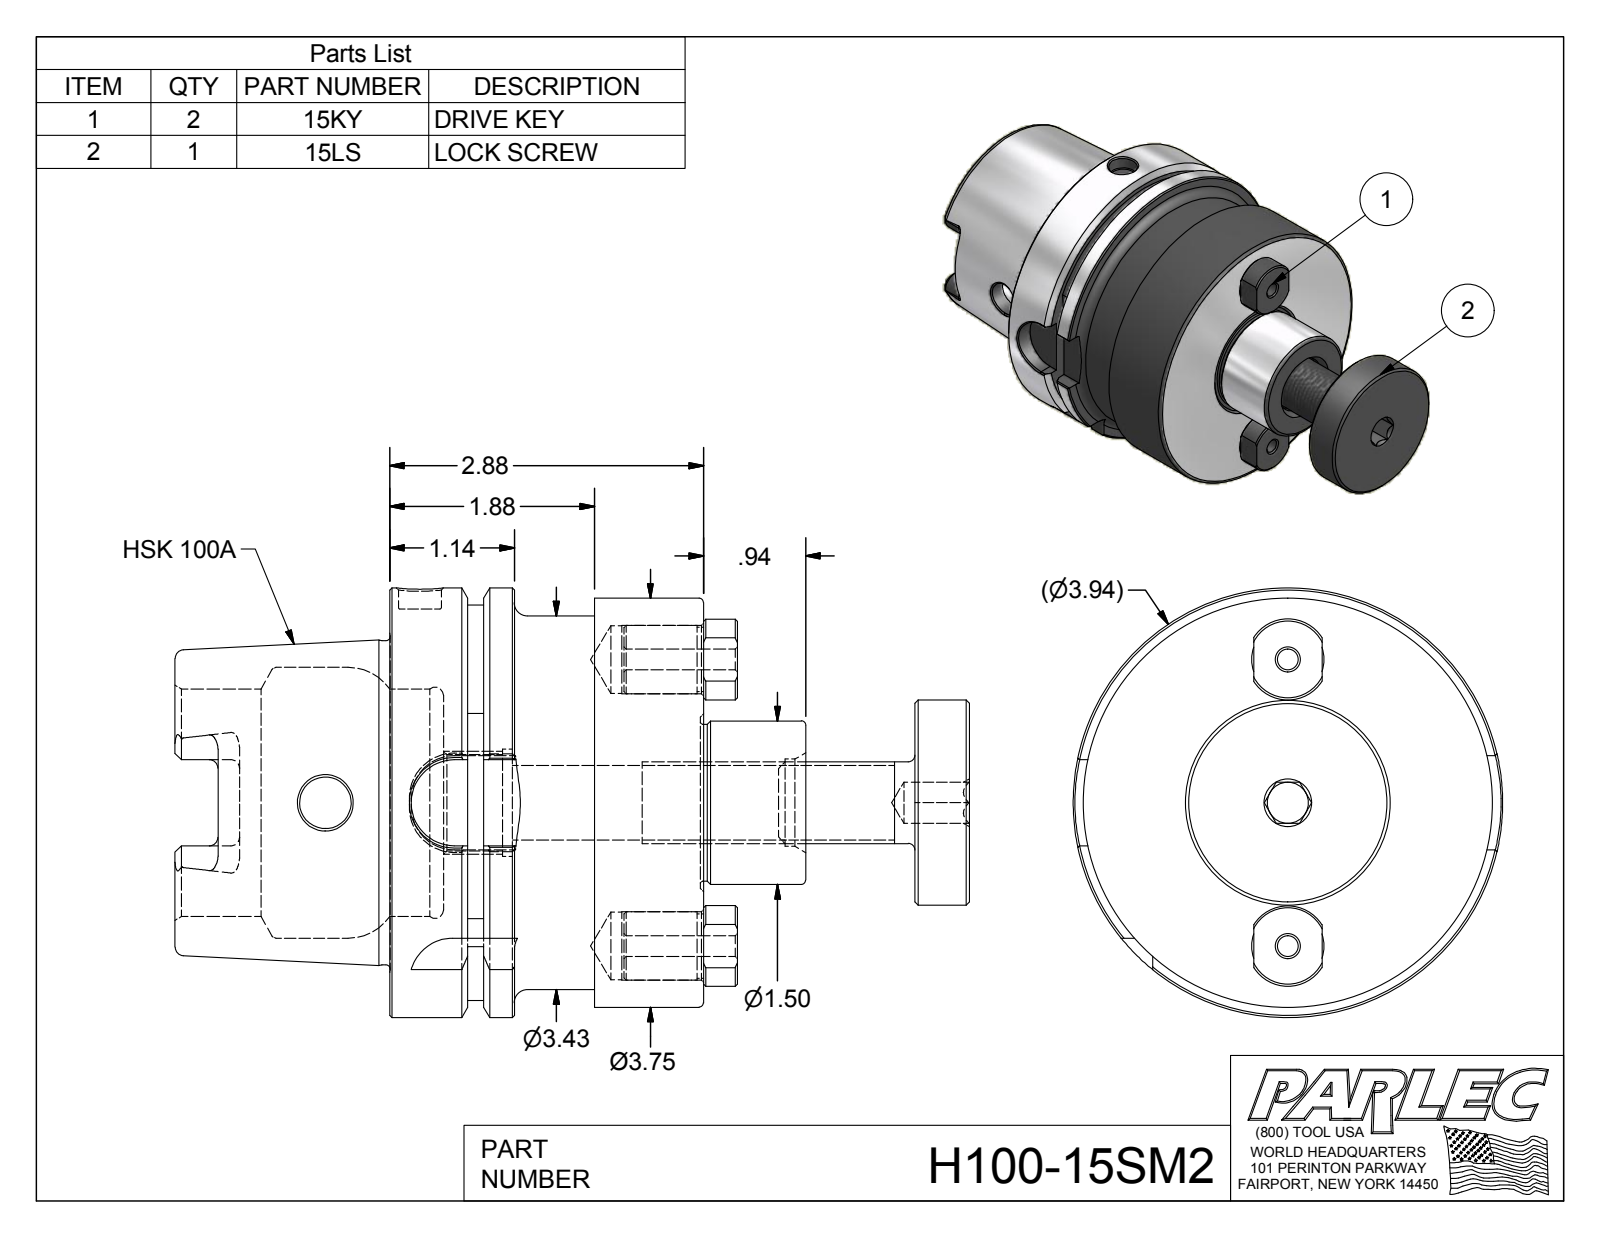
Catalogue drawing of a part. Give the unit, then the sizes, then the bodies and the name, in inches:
Units: inches
Overall size (bounding box): 7.281 × 3.937 × 3.937
Round holes (diameter × count): ⌀0.19 ×2, ⌀0.618 ×2, ⌀0.624 ×2, ⌀0.375 ×1, ⌀0.394 ×1, ⌀0.472 ×1, ⌀0.682 ×1, ⌀0.8 ×1, ⌀0.881 ×1, ⌀0.985 ×1, ⌀2.087 ×1, ⌀2.48 ×1
Round bosses / shafts (diameter × count): ⌀0.626 ×2, ⌀0.59 ×2, ⌀3.937 ×1, ⌀3.75 ×1, ⌀3.425 ×1, ⌀2.967 ×1, ⌀1.88 ×1, ⌀1.5 ×1
Partial cylindrical surfaces — rounded edges, fillets, slot ends (radius × count): R0.079 ×6, R0.192 ×4, R0.394 ×4, R0.37 ×2, R1.811 ×1
Main face-to-face distances: 2.875, 1.937, 1, 0.492, 5.312, 2.437, 2.383, 4.82, 4.812, 4.32
Hole centre spacings: 1.312, 2.624
Volume: 35.86 in³ · Surface area: 132.2 in²
Bodies: 4 solids, 213 faces (79 planar, 59 cylindrical, 75 other)
Part name (STEP PRODUCT): H100-15SM2; H100-15SM2-1; 15KY; 15LS
STEP written by: Autodesk Inventor 2012 (AUTOMOTIVE_DESIGN)
